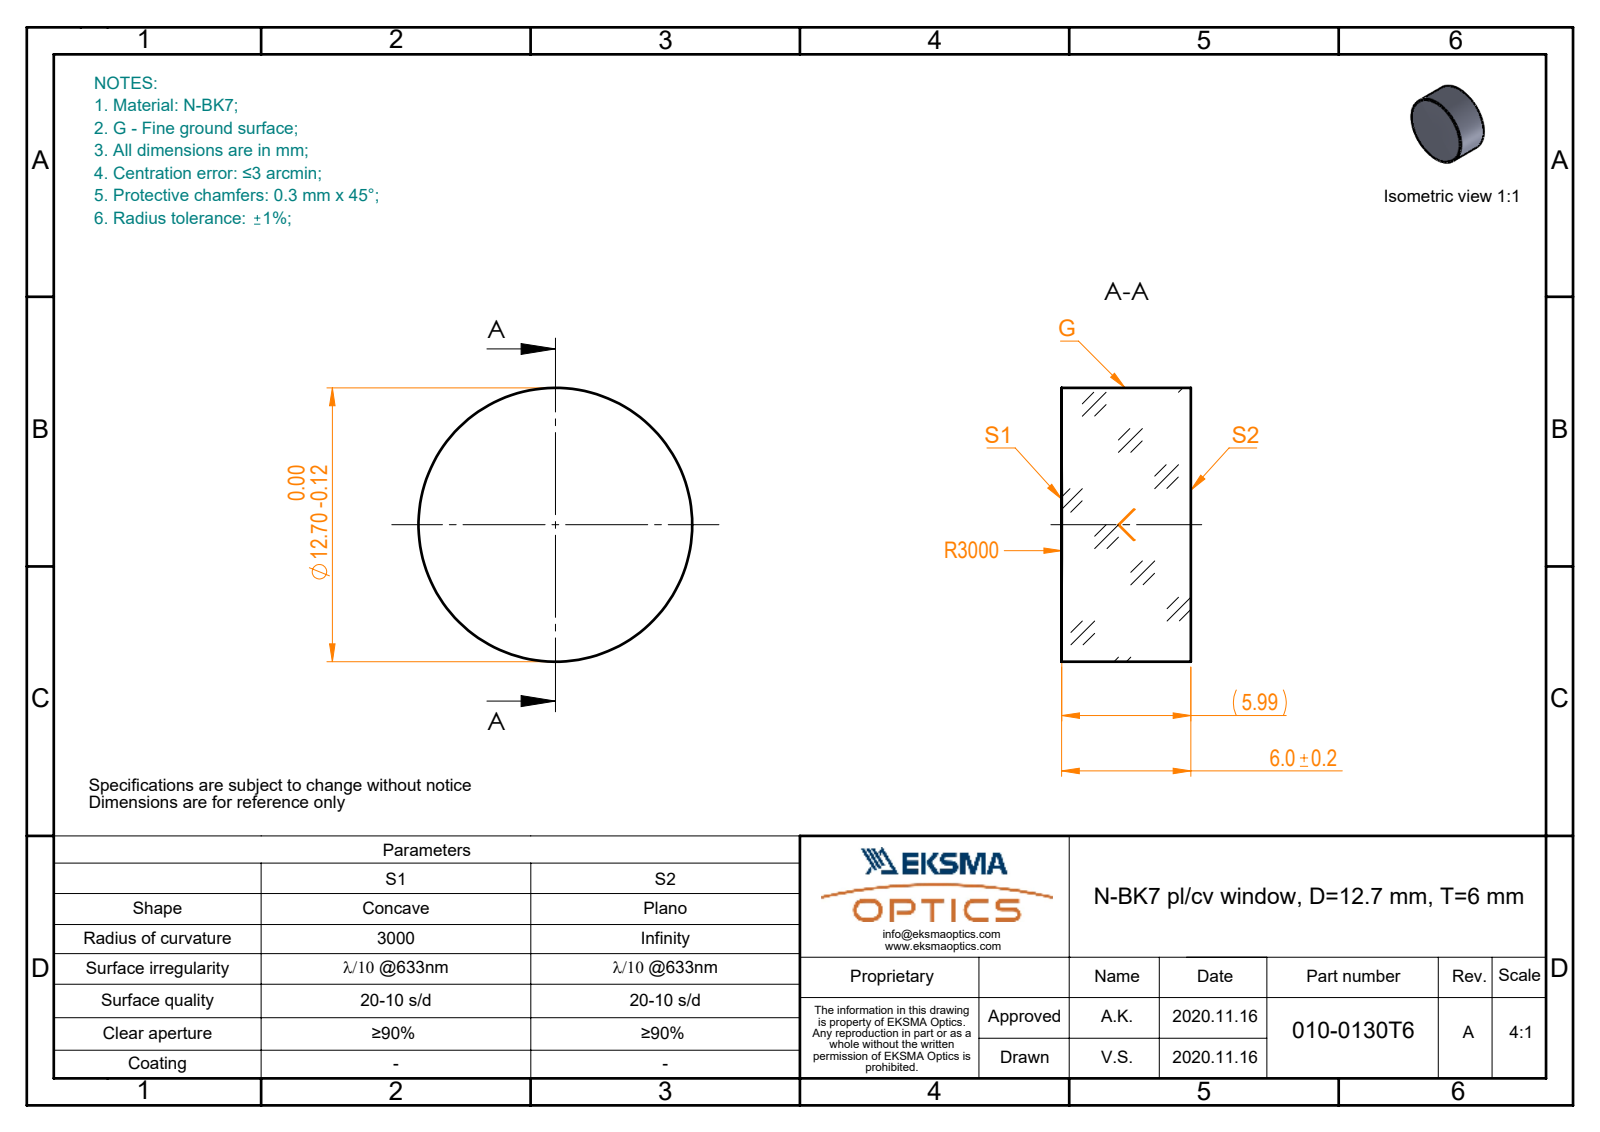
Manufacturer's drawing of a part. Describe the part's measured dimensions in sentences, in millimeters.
The part is named "010-0130T6_N-BK7_PCV_window". Its 3-D file was written by "SolidWorks 2019 (CONFIG_CONTROL_DESIGN)". It is 1 solid with 5 faces: 1 planar, 2 cylindrical and 2 other. Overall it measures 12.7 by 12.7 by 6 millimeters. Its volume is 760 cubic millimeters and its surface area 493 square millimeters. Round bosses or shafts: 1 of diameter 12.7.
